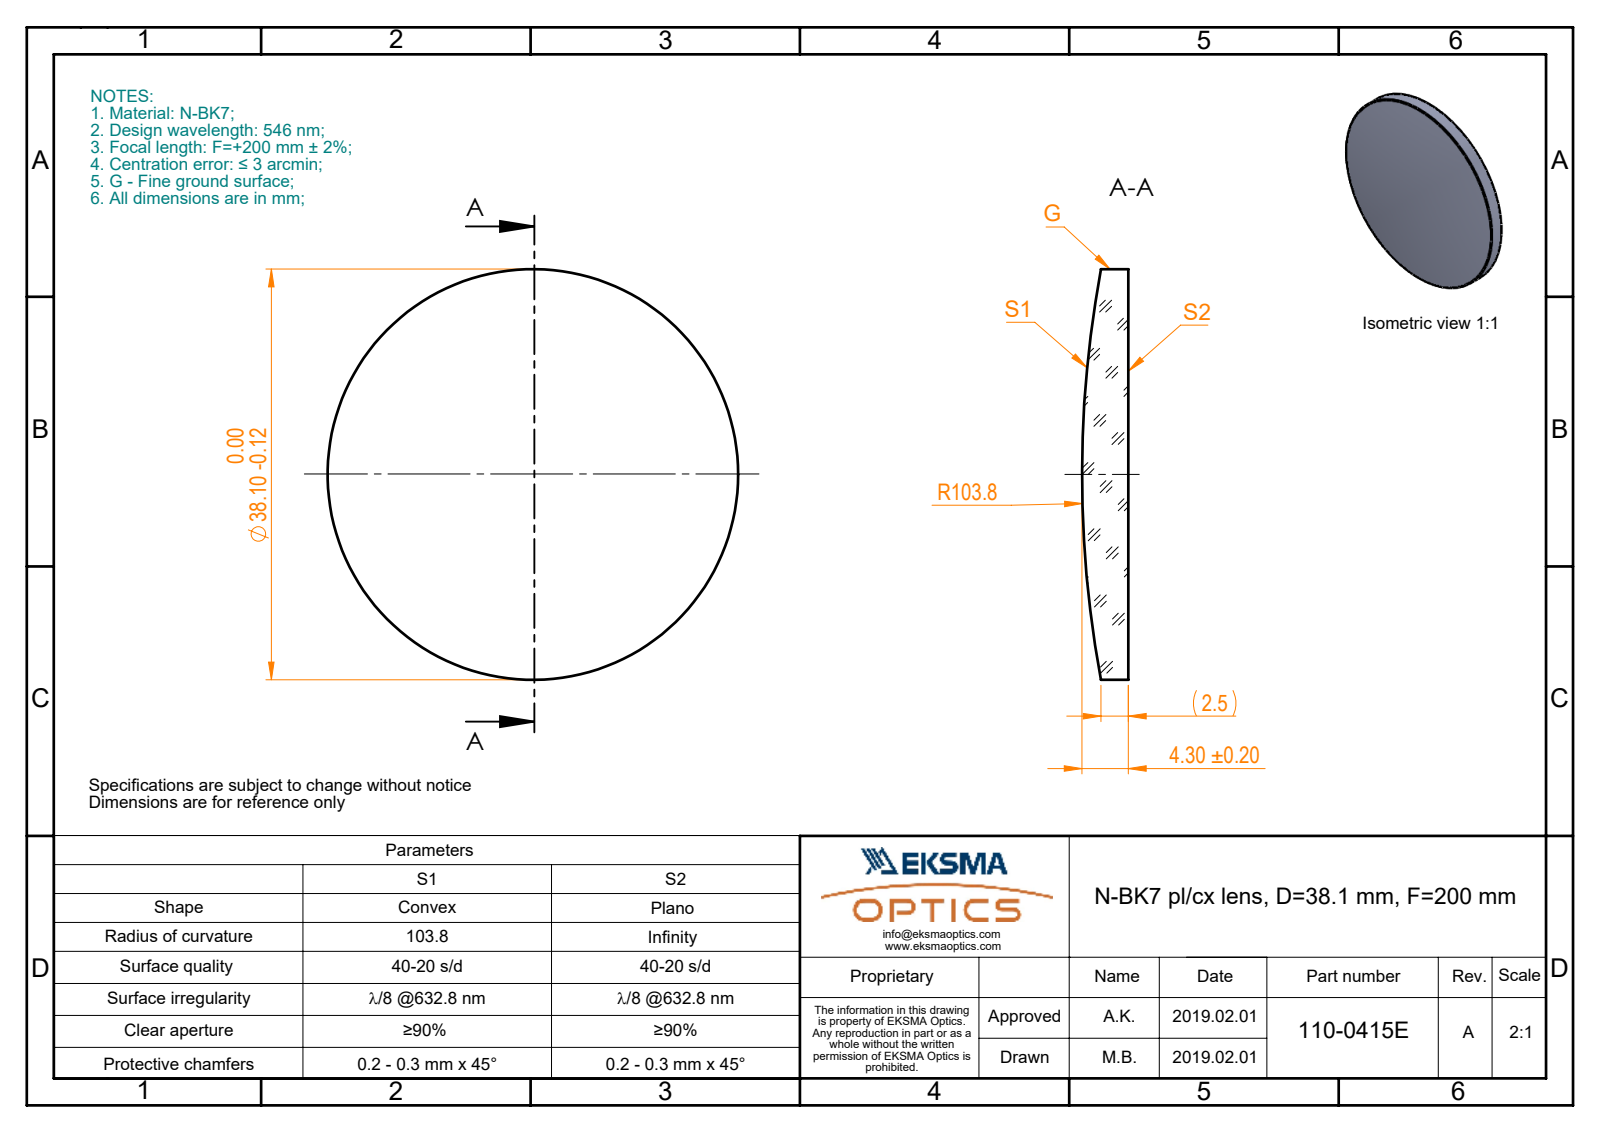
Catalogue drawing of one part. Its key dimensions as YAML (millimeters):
part_name: "110-0415E BK7 pl-cx 38.1 F200"
step_written_by: "SolidWorks 2017 (CONFIG_CONTROL_DESIGN)"
units: millimeters
bodies: {solids: 1, faces: 5, planar: 1, cylindrical: 2, other: 2}
overall_size: [38.1, 38.1, 4.3]
volume: 3900
surface_area: 2594
round_bosses_or_shafts:
  - {diameter: 38.1, count: 1}
